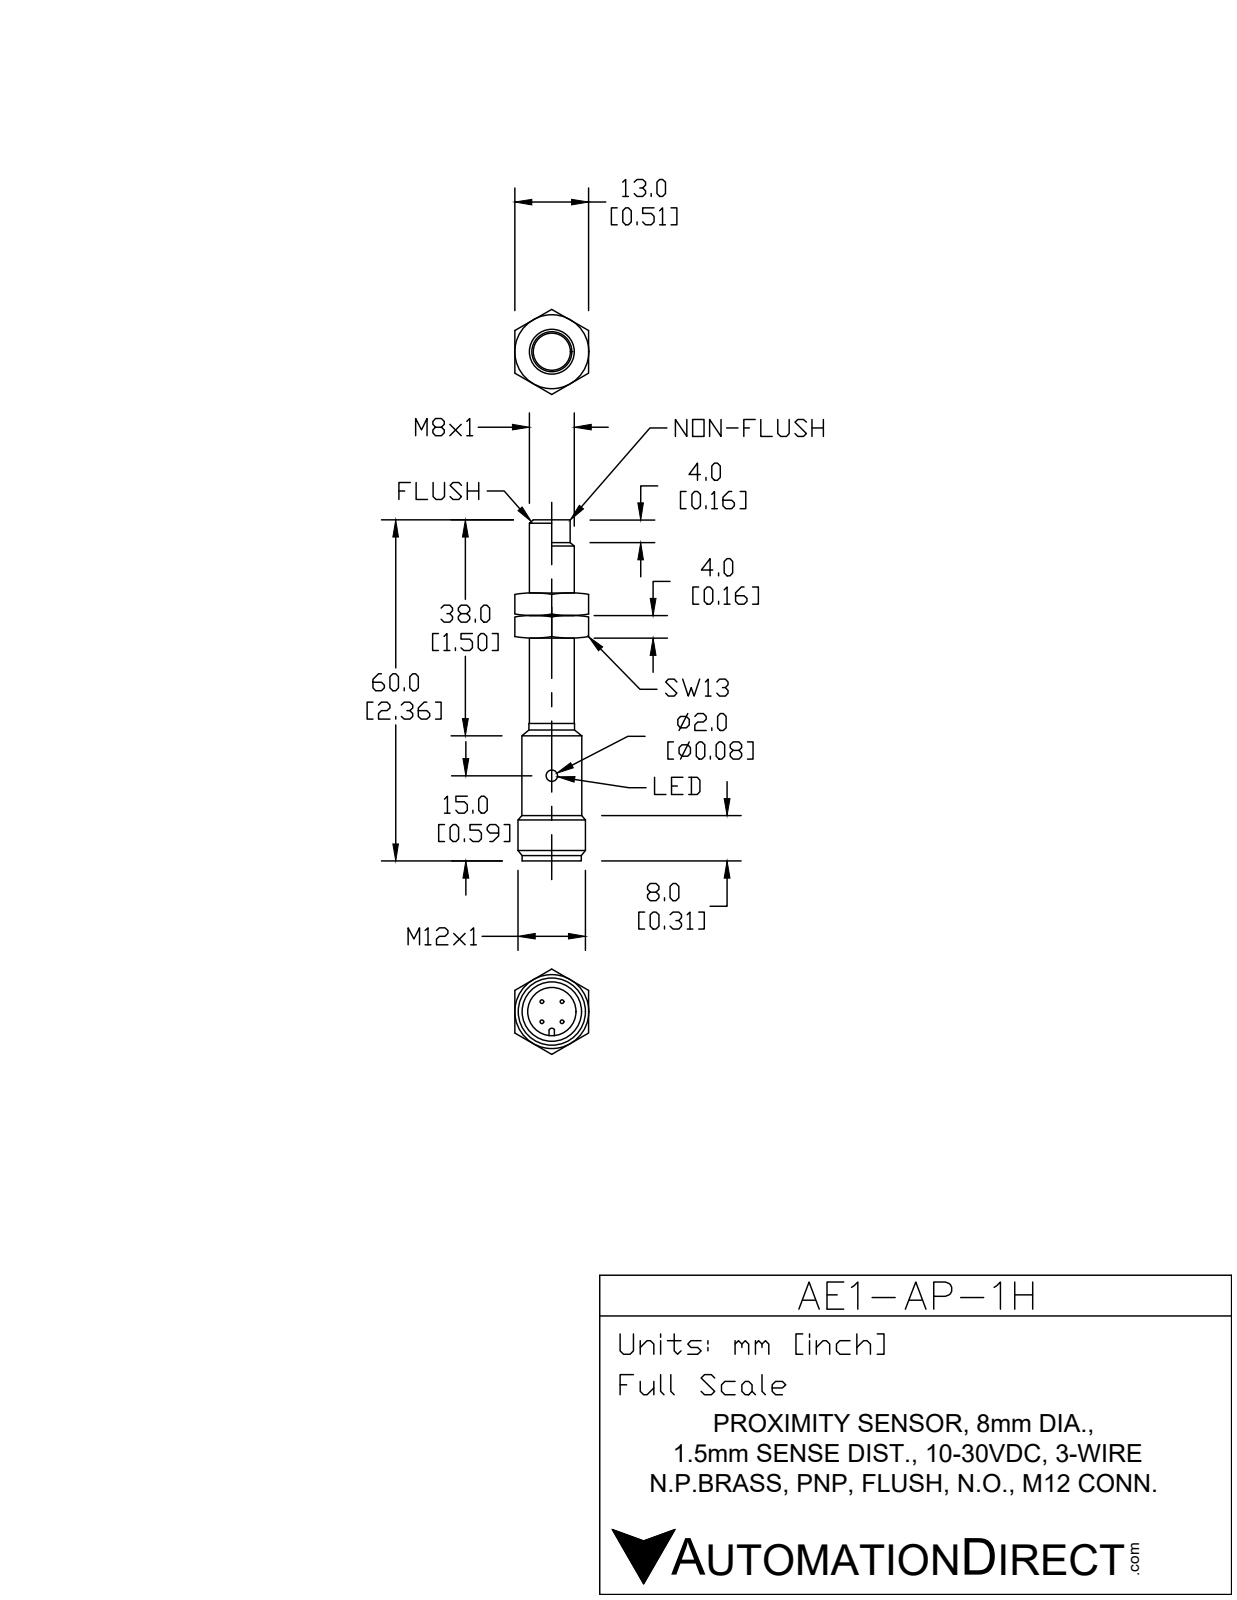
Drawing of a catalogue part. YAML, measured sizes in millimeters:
part_name: "AE1-AP-1H"
step_written_by: "SolidWorks 2017 (AUTOMOTIVE_DESIGN)"
units: millimeters
bodies: {solids: 7, faces: 137, planar: 33, cylindrical: 74, other: 30}
overall_size: [59.9, 12, 12]
volume: 3360
surface_area: 3236
round_holes:
  - {diameter: 1, count: 4}
  - {diameter: 2, count: 2}
  - {diameter: 6.2, count: 1}
  - {diameter: 8.4, count: 1}
  - {diameter: 9.9, count: 1}
round_bosses_or_shafts:
  - {diameter: 1.1, count: 4}
  - {diameter: 12, count: 1}
  - {diameter: 10.5, count: 1}
  - {diameter: 9.7, count: 1}
  - {diameter: 9.6, count: 1}
  - {diameter: 8, count: 1}
  - {diameter: 6.5, count: 1}
  - {diameter: 1, count: 1}
partial_cylinders:
  - {radius: 1.3, count: 4}
  - {radius: 0.6, count: 1}
  - {radius: 1.3, count: 1}
  - {radius: 3.4, count: 1}
face_to_face_distances: [0.4, 8.9, 48.8, 49.2, 48.5, 48.9, 4.5, 4.2, 44.3, 44.7]
hole_center_spacings: [2.5, 3.5, 5]
